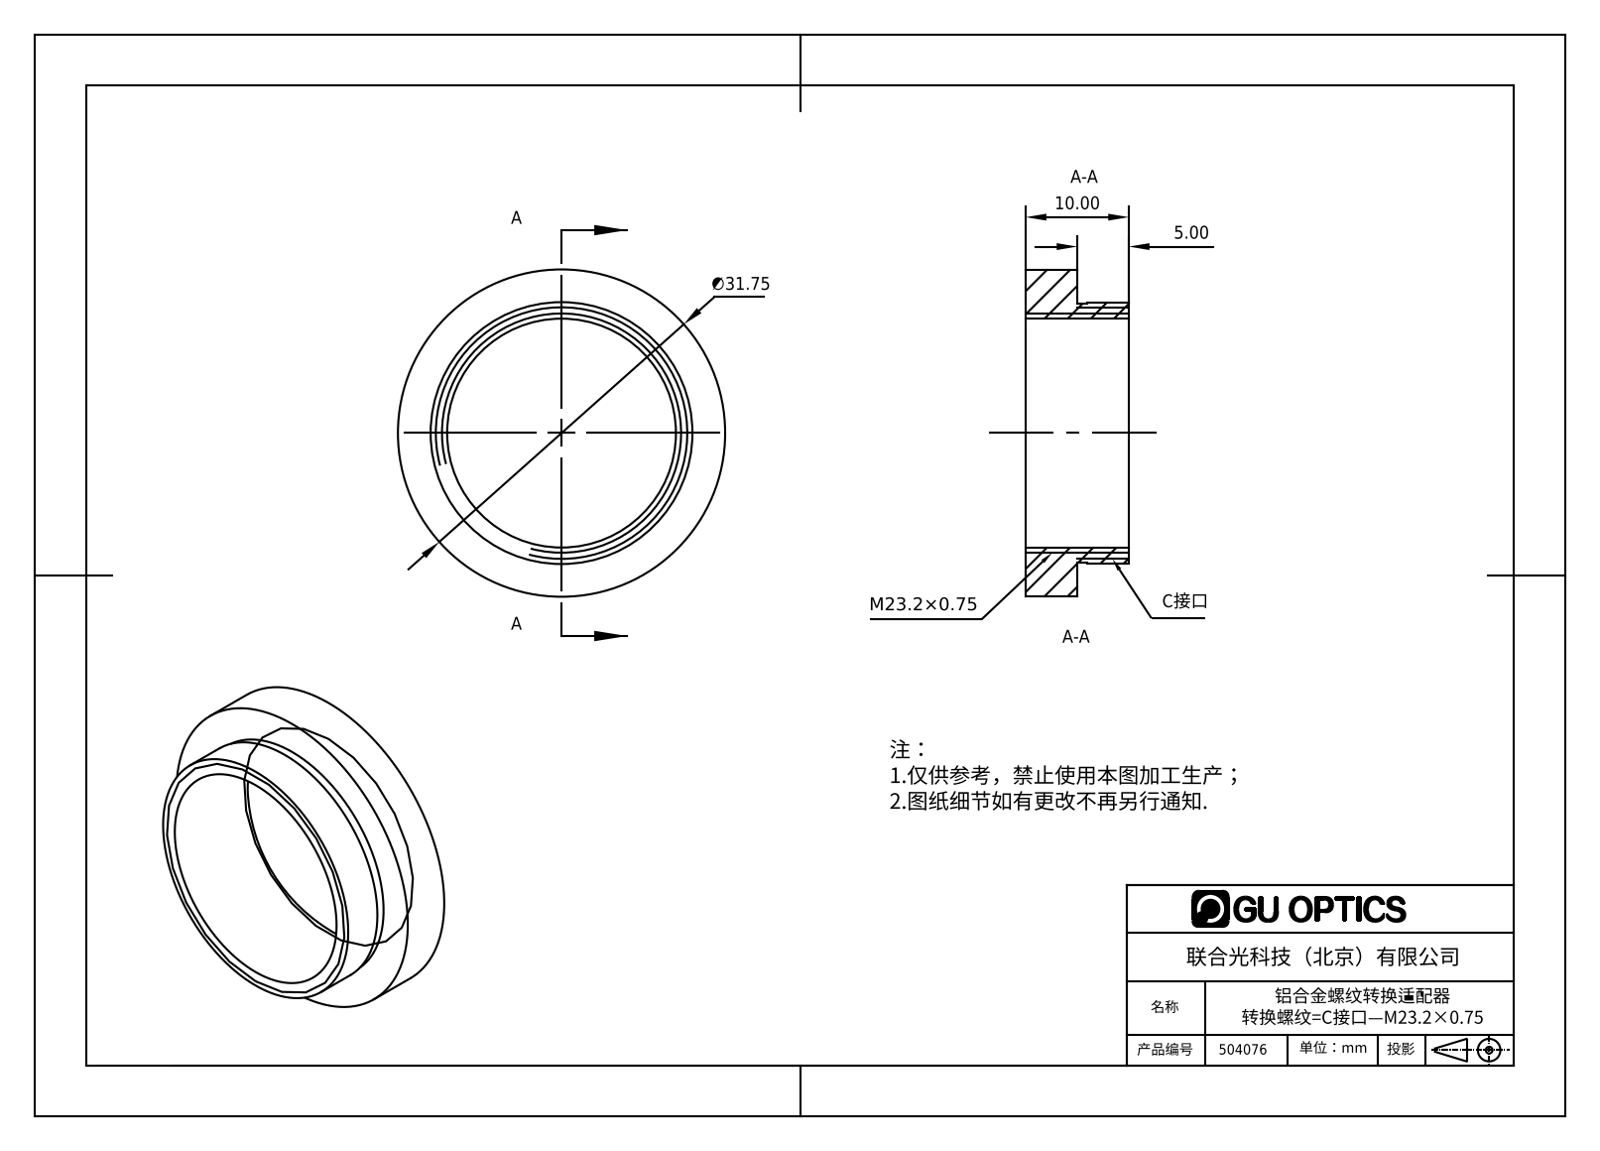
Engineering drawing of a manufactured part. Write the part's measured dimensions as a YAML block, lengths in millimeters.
part_name: "504076"
step_written_by: "SolidWorks 2016 (AUTOMOTIVE_DESIGN)"
units: millimeters
bodies: {solids: 1, faces: 12, planar: 4, cylindrical: 8, other: 0}
overall_size: [31.75, 31.75, 10]
volume: 2610
surface_area: 2427
round_holes:
  - {diameter: 22.2, count: 1}
round_bosses_or_shafts:
  - {diameter: 31.75, count: 1}
  - {diameter: 25.4, count: 1}
  - {diameter: 25.1, count: 1}
face_to_face_distances: [5, 10, 6, 1, 4]
